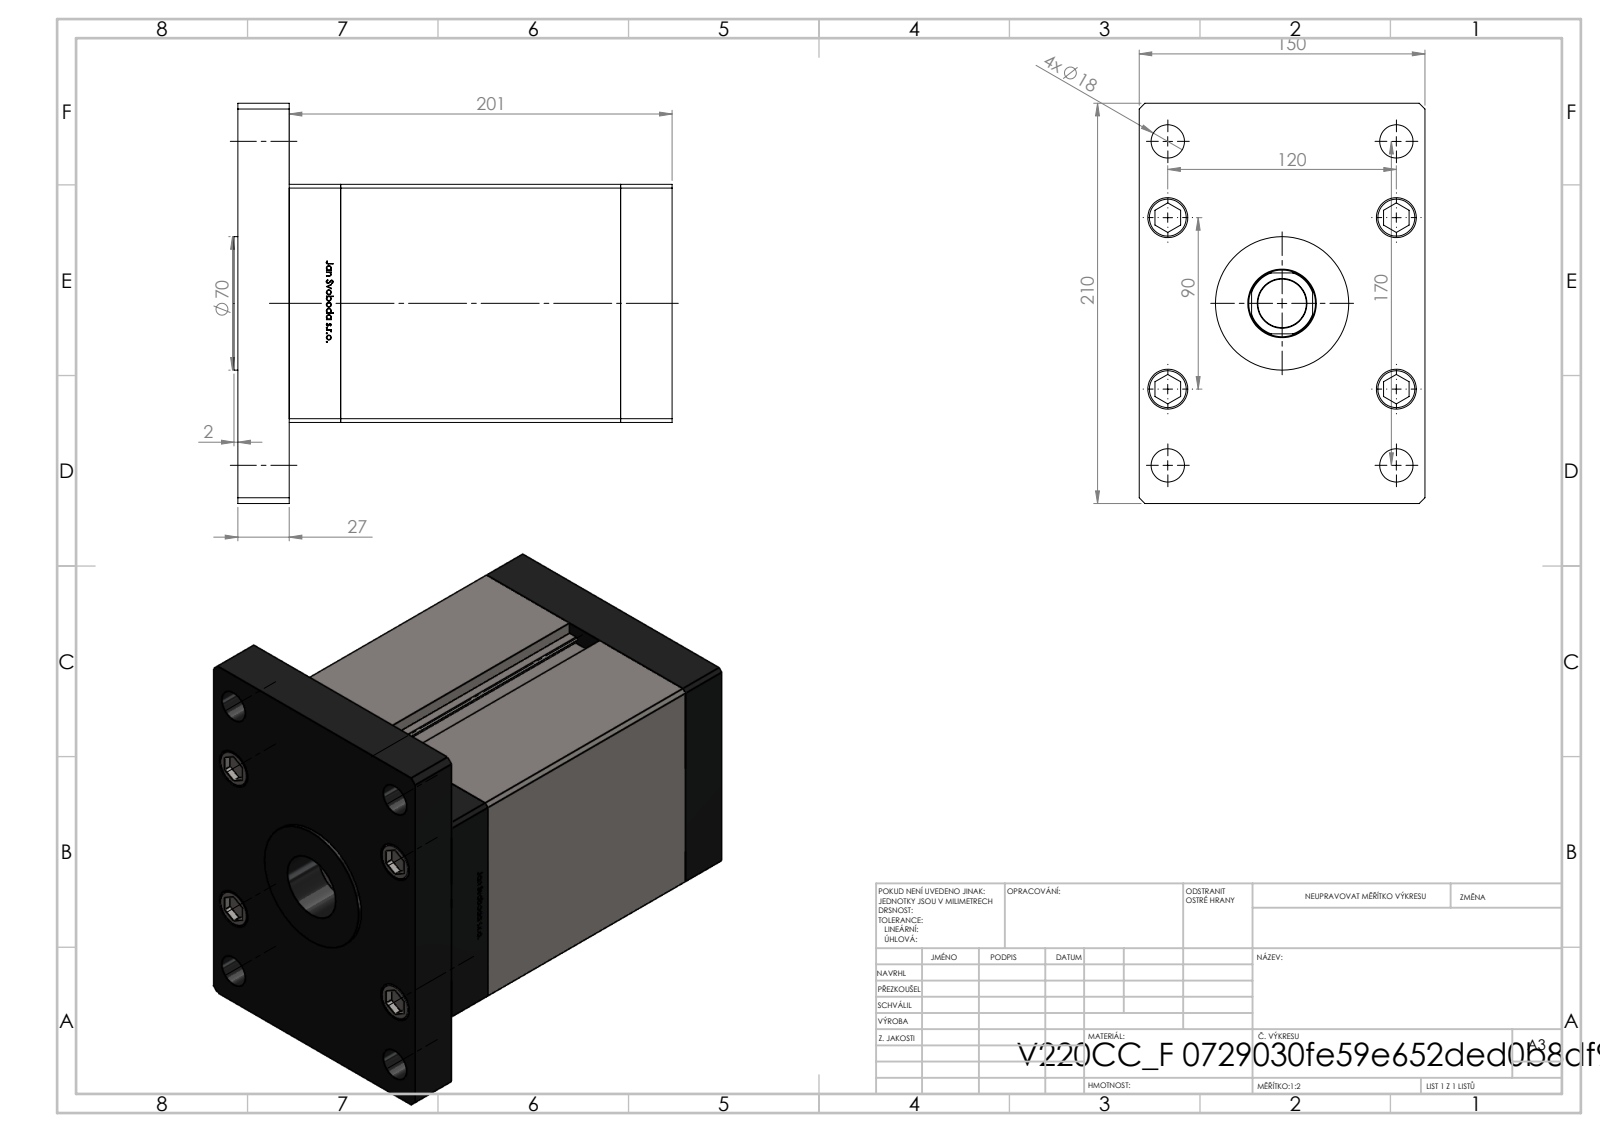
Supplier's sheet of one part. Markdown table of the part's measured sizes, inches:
| quantity | value |
| --- | --- |
| part name | V220C_F_MIDDLE; V220C_VC_F; ALLEN BOLT; V220C_F (+2 more) |
| STEP written by | SolidWorks 2019 (CONFIG_CONTROL_DESIGN) |
| units | inches |
| bodies | 19 solids, 1310 faces (517 planar, 187 cylindrical, 606 other) |
| overall size | 9.055 × 8.268 × 5.906 |
| volume | 243.7 in³ |
| surface area | 691.2 in² |
| round holes (diameter × count) | 0.689 × 9, 0.866 × 5, 0.63 × 4, 0.827 × 4, 0.079 × 2, 0.518 × 2, 1.004 × 1, 1.417 × 1, 1.476 × 1 |
| round bosses / shafts (diameter × count) | 0.315 × 9, 0.827 × 5, 3.15 × 1, 2.756 × 1 |
| partial cylindrical surfaces (radius × count) | 0.037 × 2, 0.689 × 1 |
| main face-to-face distances | 1.063, 6.85, 7.913, 5.906, 4.921, 5.787, 2.126, 8.976, 1.37, 0.307 |
| hole center spacings | 2.008, 1.575, 2.953, 4.096, 4.724, 4.98, 5.118, 6.965 |
